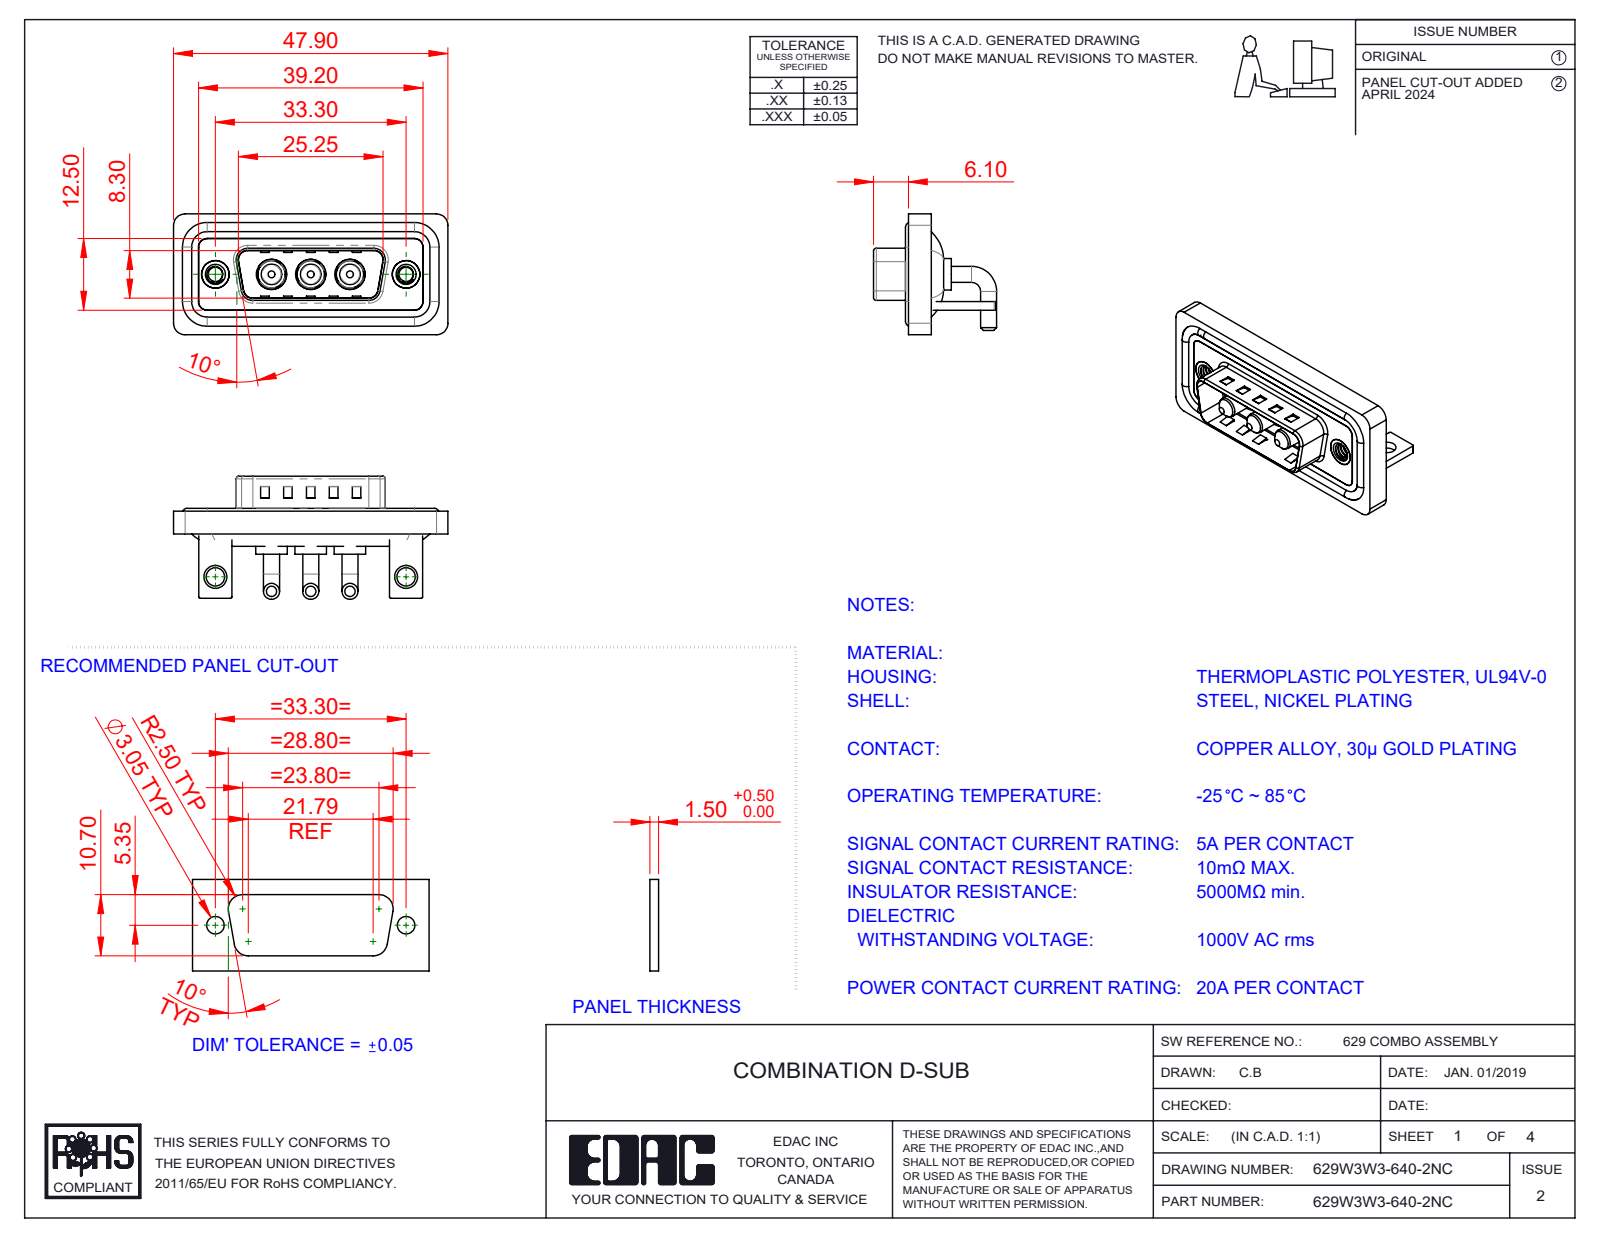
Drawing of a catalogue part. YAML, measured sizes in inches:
part_name: "629W3W3-640-2NC; Power Pin_20A RA; 629Combo Shell Rear_15 Contacts; 629Combo Stabilizer Bracket (+4 more)"
step_written_by: "SolidWorks 2023 (CONFIG_CONTROL_DESIGN)"
units: inches
bodies: {solids: 15, faces: 614, planar: 227, cylindrical: 265, other: 122}
overall_size: [1.886, 0.846, 0.831]
volume: 0.369
surface_area: 14.92
round_holes:
  - {diameter: 0.191, count: 3}
  - {diameter: 0.209, count: 3}
  - {diameter: 0.098, count: 2}
  - {diameter: 0.126, count: 2}
  - {diameter: 0.157, count: 2}
  - {diameter: 0.189, count: 2}
  - {diameter: 0.197, count: 2}
round_bosses_or_shafts:
  - {diameter: 0.11, count: 6}
  - {diameter: 0.063, count: 4}
  - {diameter: 0.217, count: 3}
  - {diameter: 0.205, count: 3}
  - {diameter: 0.187, count: 3}
  - {diameter: 0.148, count: 3}
  - {diameter: 0.142, count: 3}
  - {diameter: 0.193, count: 2}
partial_cylinders:
  - {radius: 0.079, count: 21}
  - {radius: 0.059, count: 18}
  - {radius: 0.01, count: 16}
  - {radius: 0.02, count: 9}
  - {radius: 0.063, count: 8}
  - {radius: 0.024, count: 4}
  - {radius: 0.026, count: 4}
  - {radius: 0.035, count: 4}
face_to_face_distances: [0.016, 0.059, 0.031, 0.114, 0.043, 0.083, 0.146, 0.063, 0.047, 0.177]
hole_center_spacings: [0.27, 0.386, 0.656, 0.925, 1.311, 0.539]
